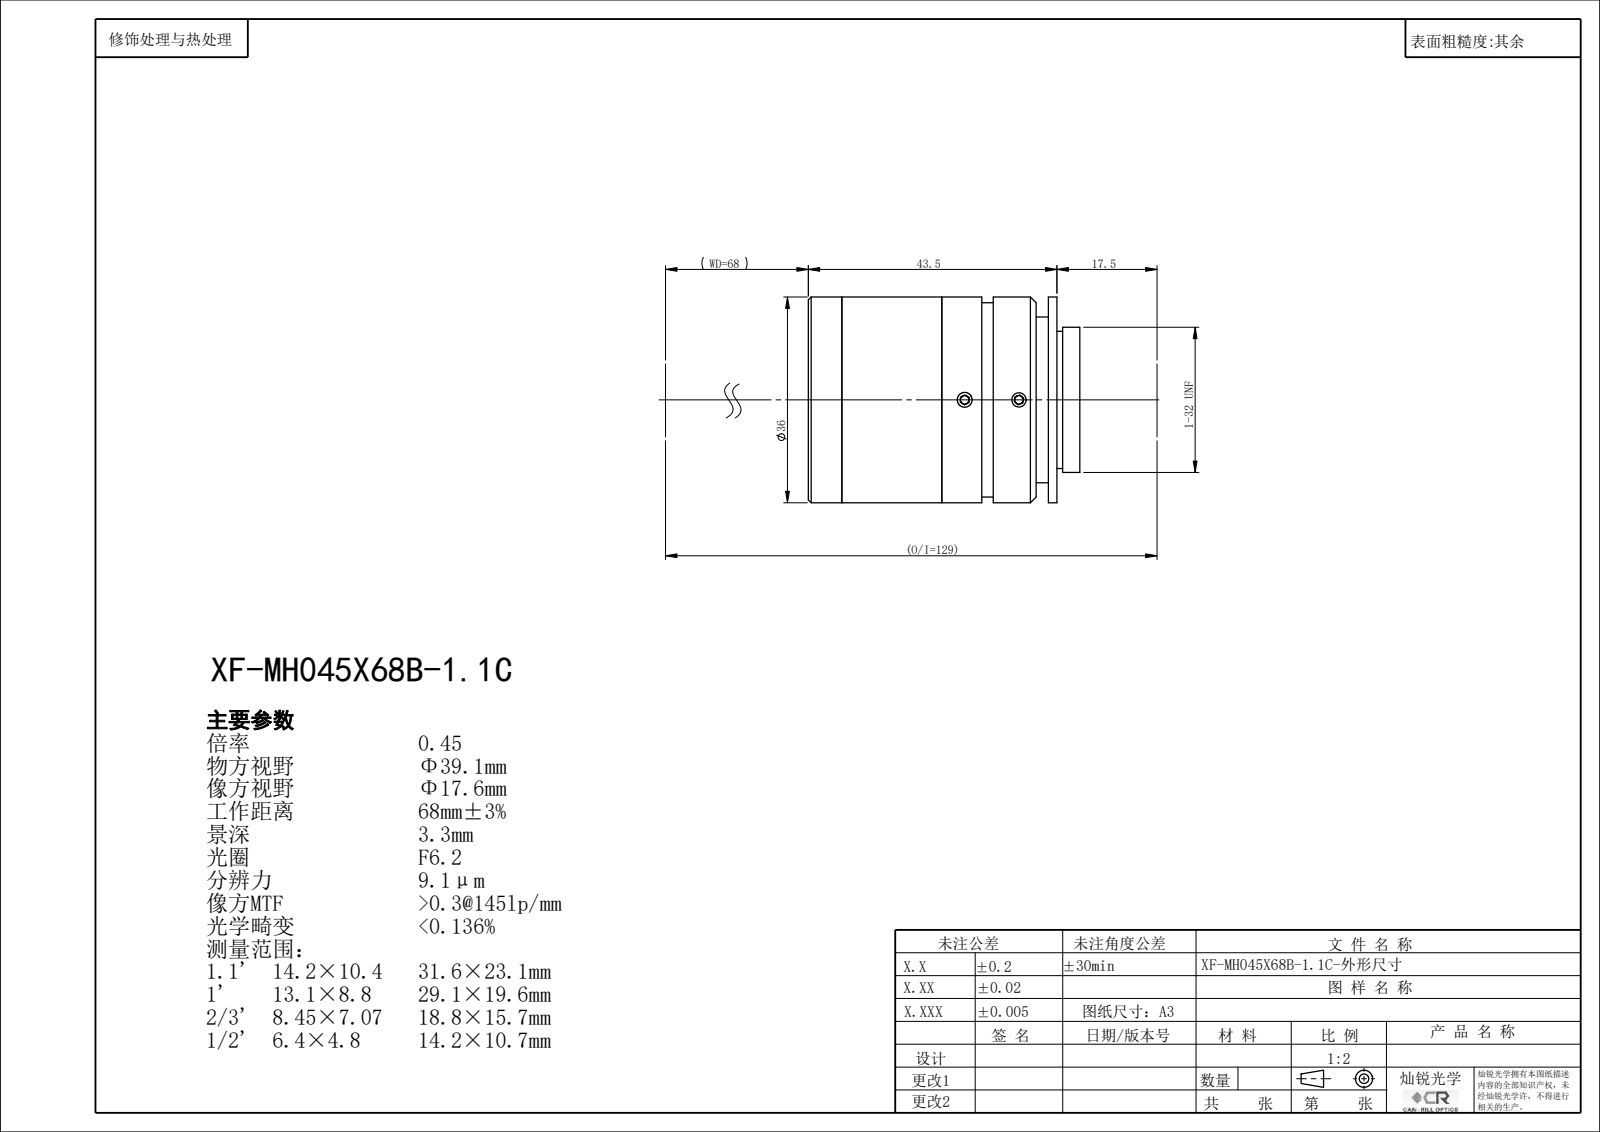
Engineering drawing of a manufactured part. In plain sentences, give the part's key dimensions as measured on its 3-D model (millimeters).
The part is named "XF-MH045X68B-1.1C". Its 3-D file was written by "SolidWorks 2022 (CONFIG_CONTROL_DESIGN)". It is 0 solids with 147 faces: 77 planar, 40 cylindrical and 30 other. Overall it measures 47.53 by 36 by 36 millimeters. Round holes: 3 of diameter 2.5, 1 of diameter 14, 1 of diameter 16.4, 1 of diameter 17, 1 of diameter 18.4, 1 of diameter 22.4, 1 of diameter 24, 1 of diameter 24.9, 1 of diameter 26. Round bosses or shafts: 1 of diameter 36, 1 of diameter 34, 1 of diameter 29, 1 of diameter 25.4. The main face-to-face distances are 20.15, 23.38, 43.53, 1.5, 42.03, 18.65, 5.88, 17.5, 36.15, 37.65.
